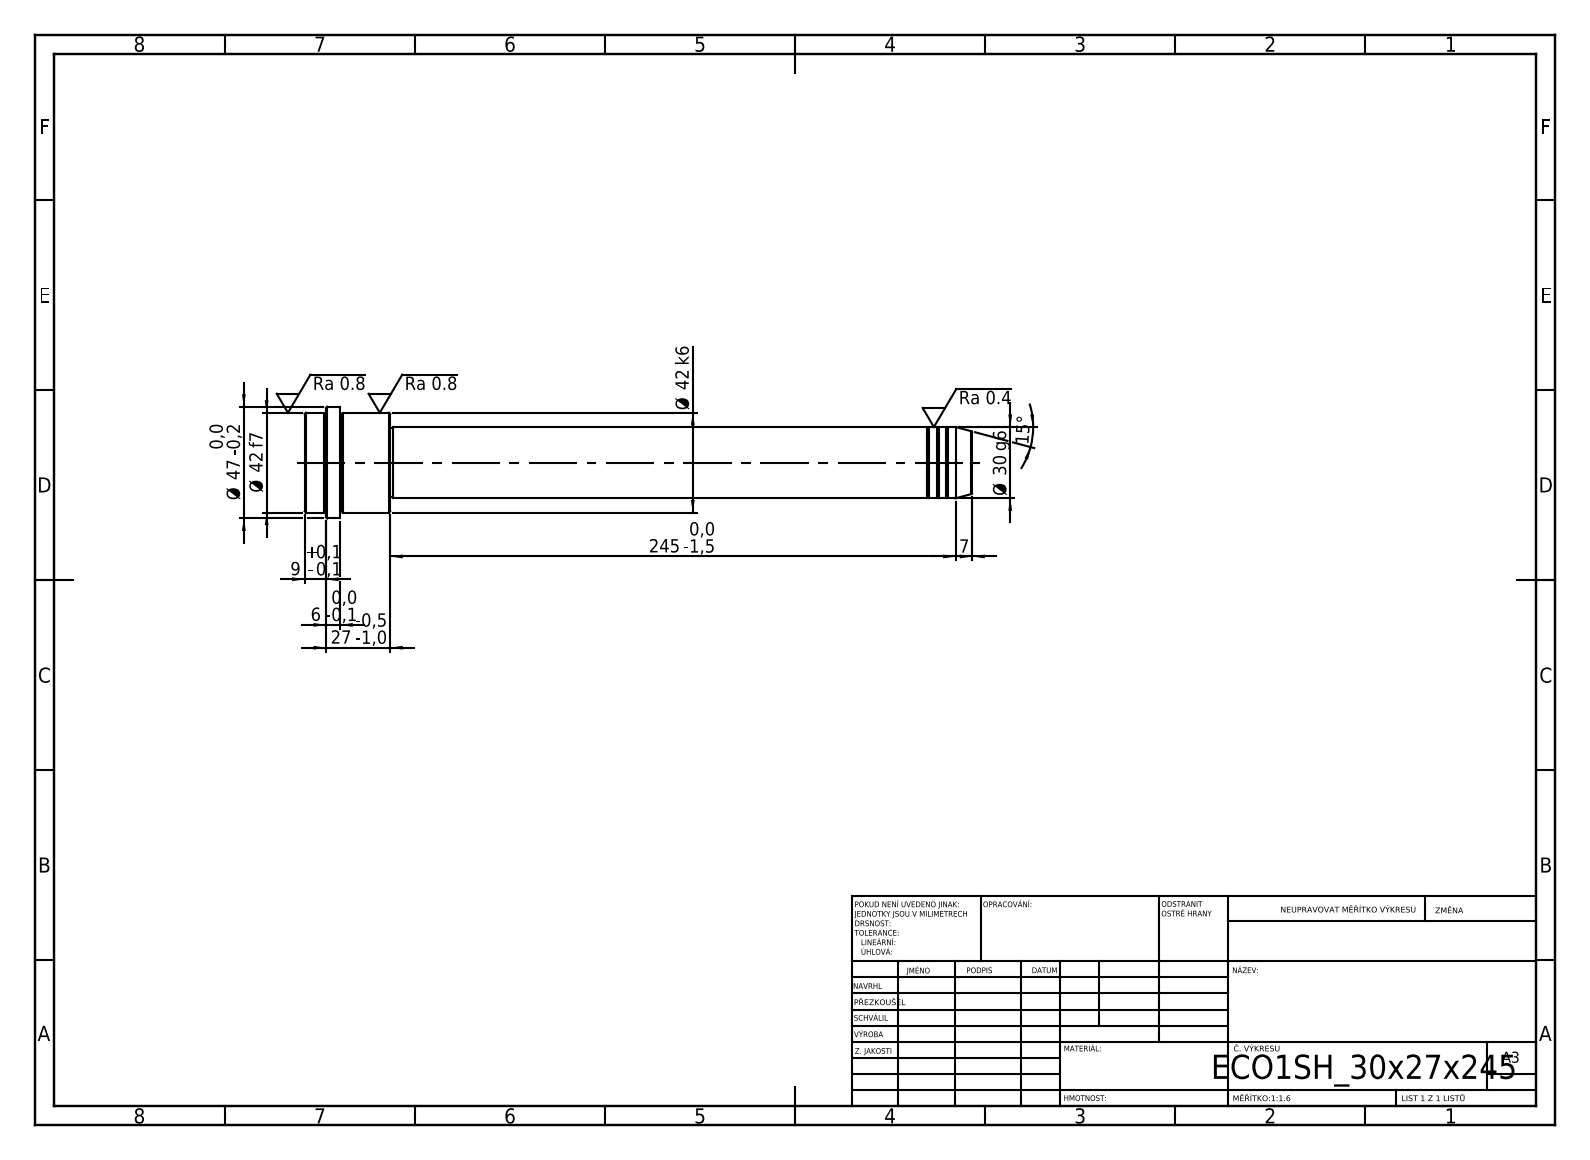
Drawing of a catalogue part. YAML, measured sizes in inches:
step_written_by: "SolidWorks 2019 (CONFIG_CONTROL_DESIGN)"
units: inches
bodies: {solids: 1, faces: 52, planar: 6, cylindrical: 16, other: 30}
overall_size: [11.063, 1.85, 1.85]
volume: 13.68
surface_area: 48.79
round_bosses_or_shafts:
  - {diameter: 1.85, count: 1}
  - {diameter: 1.654, count: 1}
  - {diameter: 1.181, count: 1}
  - {diameter: 1.142, count: 1}
face_to_face_distances: [1.417, 9.646, 11.063, 10.472, 0.827, 0.591, 10.709, 1.063, 0.236, 0.354]
